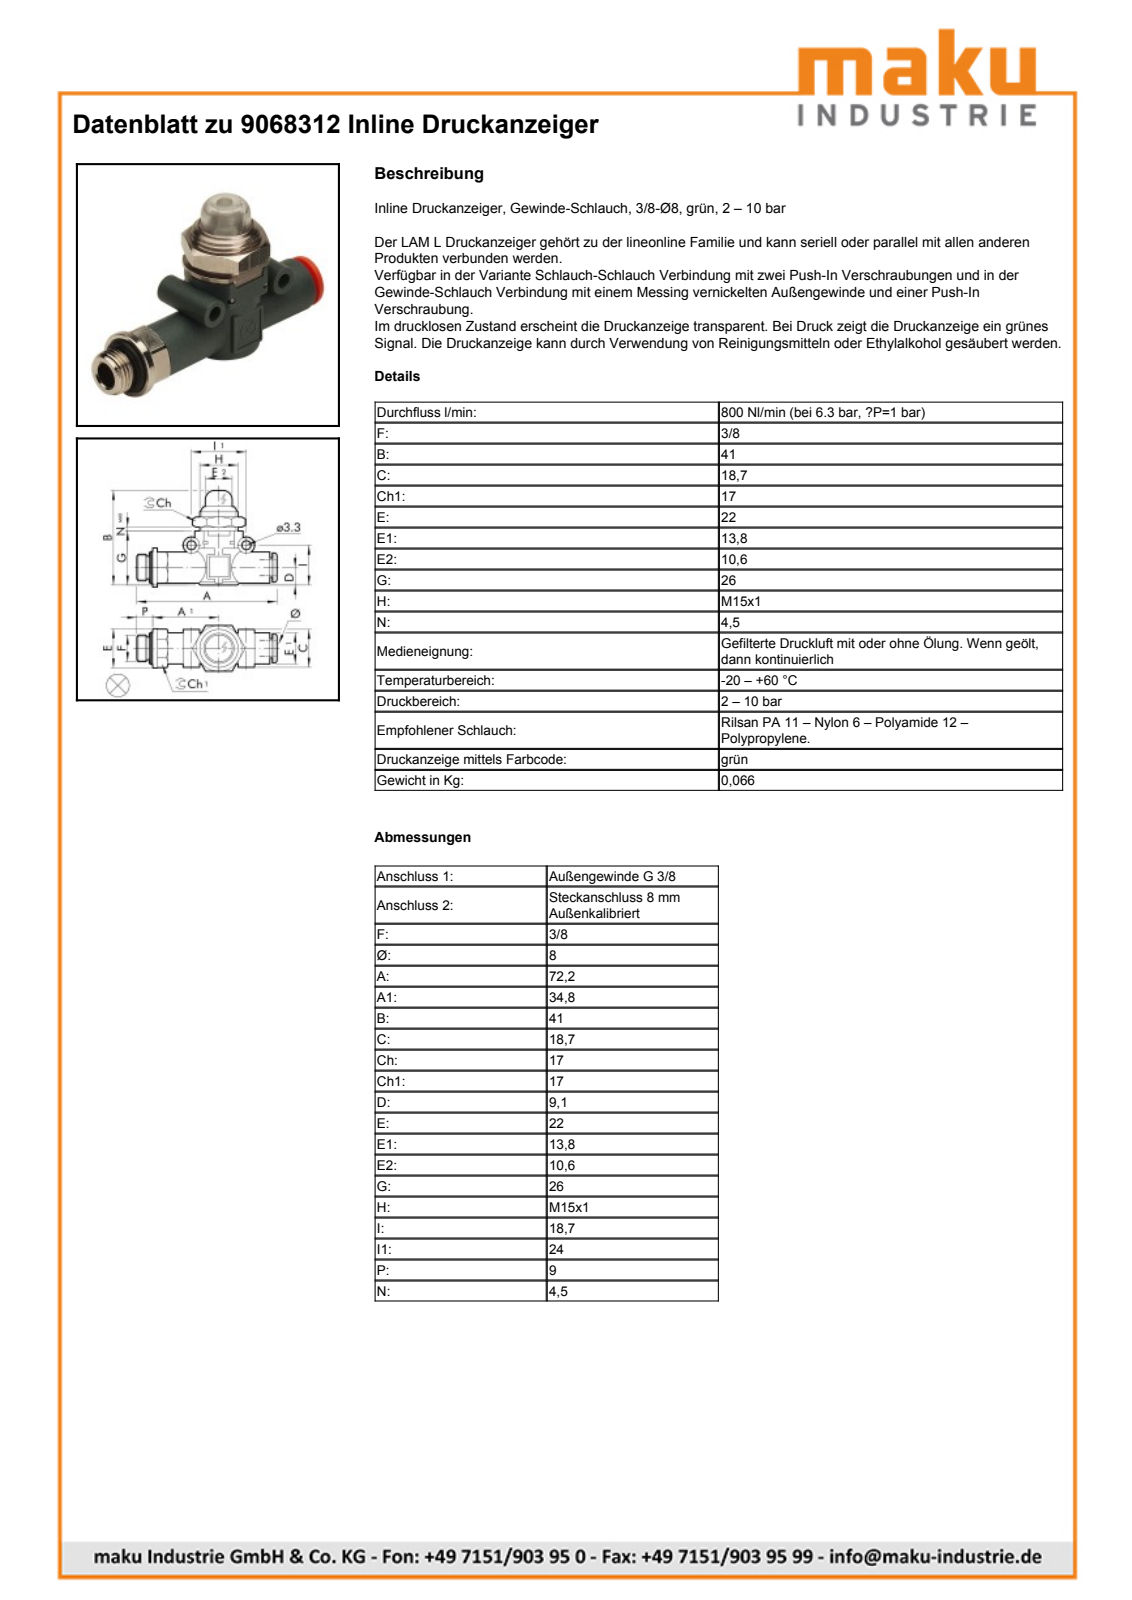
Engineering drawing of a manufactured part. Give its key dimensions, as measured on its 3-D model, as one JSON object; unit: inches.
{"part_name": "9068312; LINE-ON-LINE D8 V2v/V3V_L body; LINE-ON-LINE D8 VNR-L bushing; LINE-ON-LINE D8-3/8 thread port (+1 more)", "step_written_by": "PARTsolutions (AUTOMOTIVE_DESIGN)", "units": "inches", "bodies": {"solids": 4, "faces": 183, "planar": 94, "cylindrical": 58, "other": 31}, "overall_size": [2.843, 1.689, 0.866], "volume_in3": 0.842, "surface_area_in2": 17.43, "round_holes": [[0.13, 2], [0.236, 2], [0.217, 1], [0.319, 1], [0.394, 1], [0.433, 1], [0.459, 1], [0.492, 1], [0.591, 1]], "round_bosses_or_shafts": [[0.236, 2], [0.866, 1], [0.74, 1], [0.656, 1], [0.575, 1], [0.551, 1], [0.543, 1], [0.535, 1]], "partial_cylinders_radius": [[0.148, 1], [0.378, 1], [0.38, 1], [0.402, 1], [0.407, 1], [0.451, 1]], "face_to_face_distances": [0.949, 0.669, 0.075, 0.465, 0.161, 0.787, 0.157, 1.024, 0.862, 0.03], "hole_center_spacings": [0.605, 0.945]}
